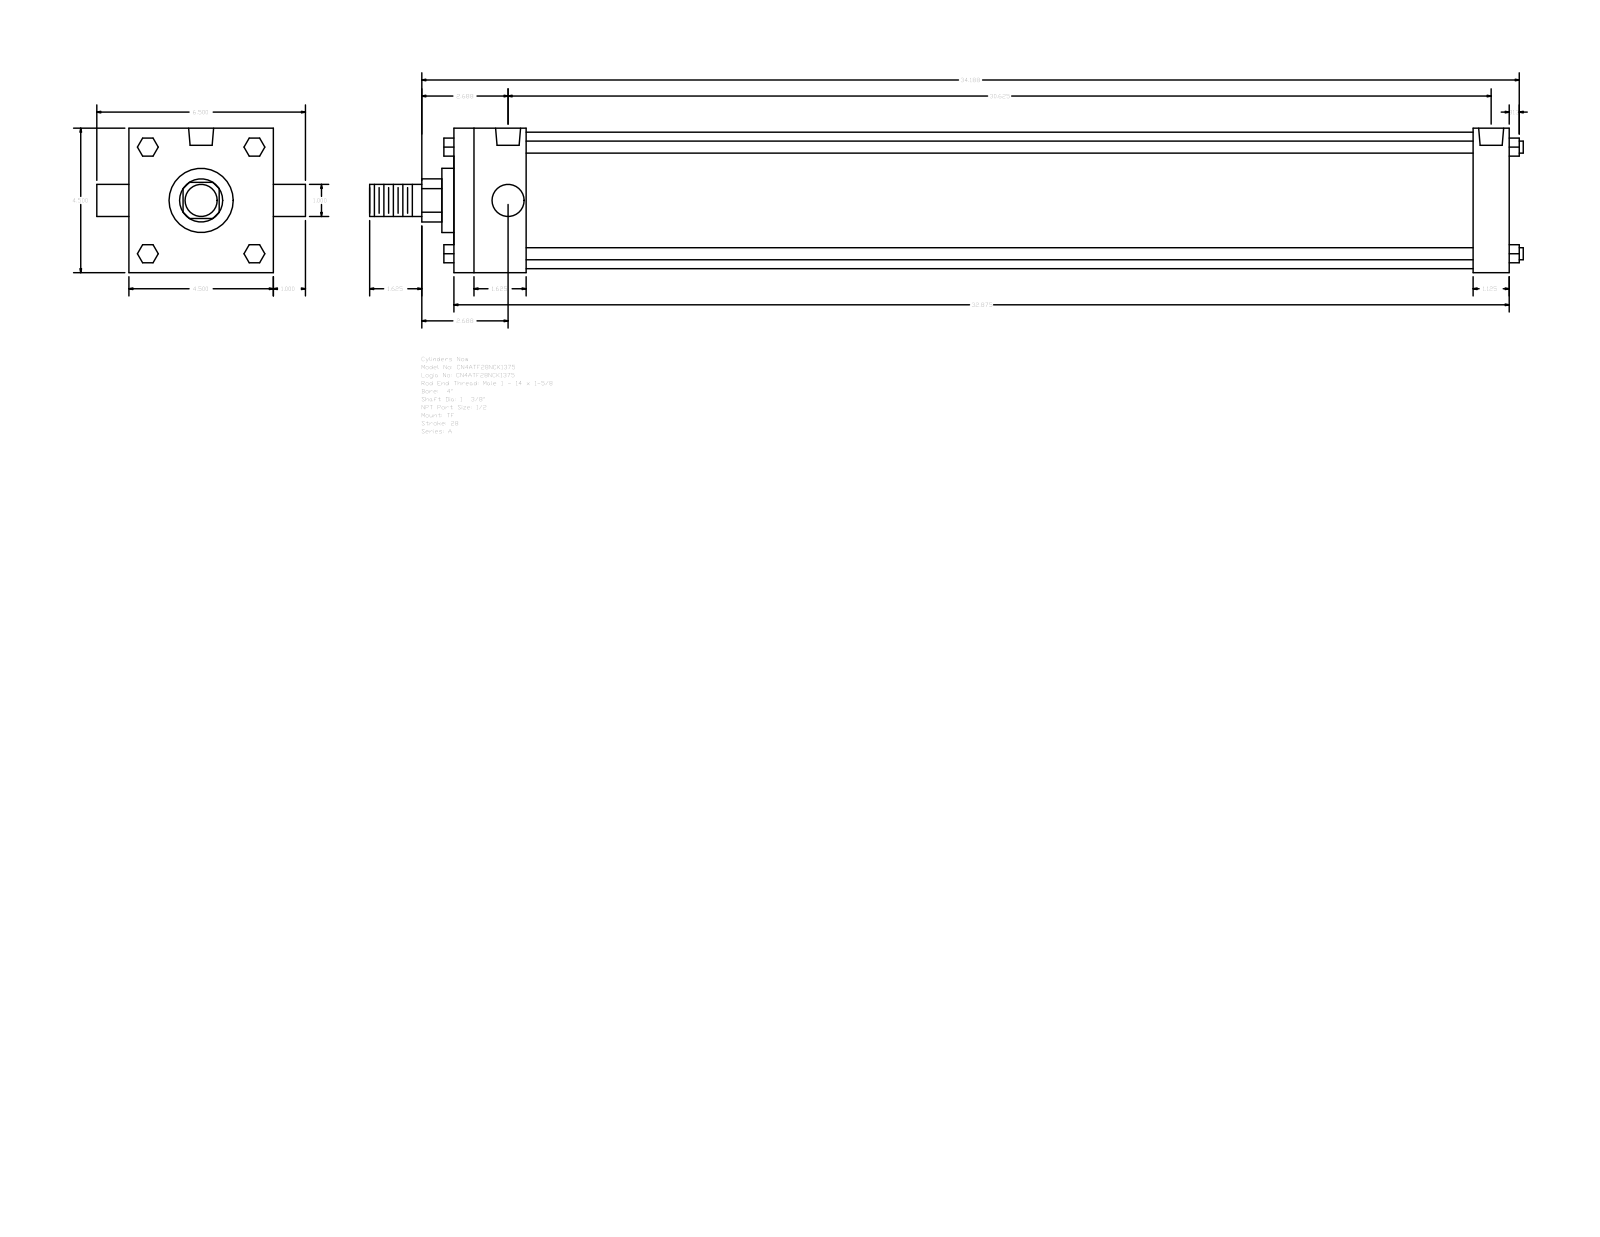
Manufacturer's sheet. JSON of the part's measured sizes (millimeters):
{"part_name": "A_TF__0400_1.375", "step_written_by": "GSSL Pune (CONFIG_CONTROL_DESIGN)", "units": "millimeters", "bodies": {"solids": 0, "faces": 120, "planar": 92, "cylindrical": 28, "other": 0}, "overall_size": [912.81, 165.1, 114.3], "round_holes": [[8.73, 3], [19.77, 2]], "round_bosses_or_shafts": [[9.53, 4], [25.4, 2], [107.95, 1], [50.8, 1], [34.92, 1]], "partial_cylinders_radius": [[17.06, 1]], "face_to_face_distances": [114.3, 835.02, 57.15, 806.45, 28.57, 749.3, 777.87, 66.67, 14.29, 25.4], "hole_center_spacings": [3.18, 774.7, 771.52, 777.88]}
